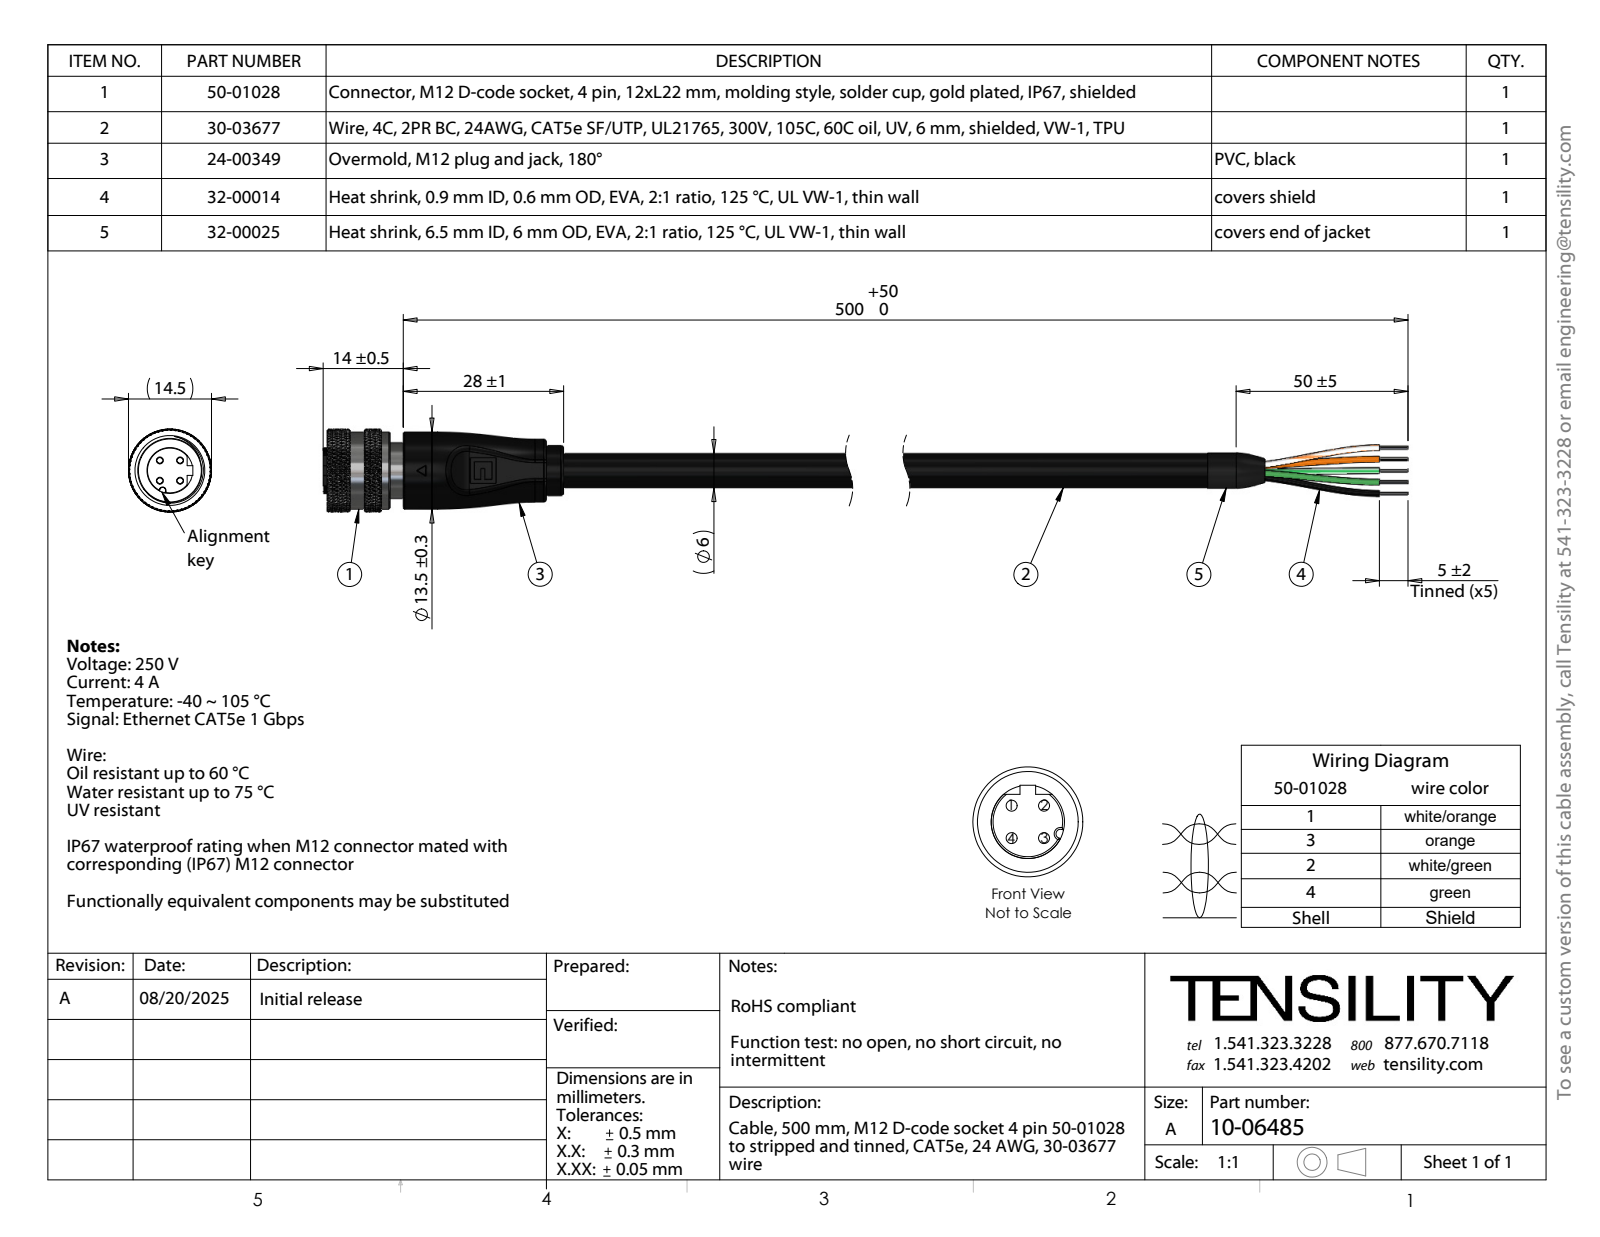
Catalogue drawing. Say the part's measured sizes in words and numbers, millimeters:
The part is named "30-03677_s + t; 50-01028_默认; 50-01028-05_默认; 24-00349_Mexico (+5 more)". Its 3-D file was written by "SolidWorks 2025 (CONFIG_CONTROL_DESIGN)". It is 87 solids with 3550 faces: 339 planar, 940 cylindrical and 2271 other. Overall it measures 222 by 14.5 by 14.5 millimeters. Its volume is 9 616 cubic millimeters and its surface area 27 027 square millimeters. Round holes: 28 of diameter 0.2, 4 of diameter 1.05, 4 of diameter 1.1, 4 of diameter 1.2, 1 of diameter 3.16, 1 of diameter 3.21, 1 of diameter 3.36, 1 of diameter 9, 1 of diameter 10, 1 of diameter 11.2. Round bosses or shafts: 35 of diameter 0.2, 4 of diameter 1.6, 4 of diameter 1.5, 1 of diameter 13.5, 1 of diameter 11, 1 of diameter 10.6, 1 of diameter 10.5, 1 of diameter 9.8. Partial cylindrical surfaces (rounded edges, fillets, slot ends): 10 of radius 0.1, 6 of radius 0.4, 2 of radius 0.5, 2 of radius 1.5, 1 of radius 4, 1 of radius 5, 1 of radius 5.58, 1 of radius 6.75. The main face-to-face distances are 178, 28, 150, 7, 4.7, 1, 31.8, 3.5, 23.3, 173.3. The hole center spacings are 1.91, 0.36, 2.09, 1.06, 0.89, 1.08, 1.24, 1.8.
